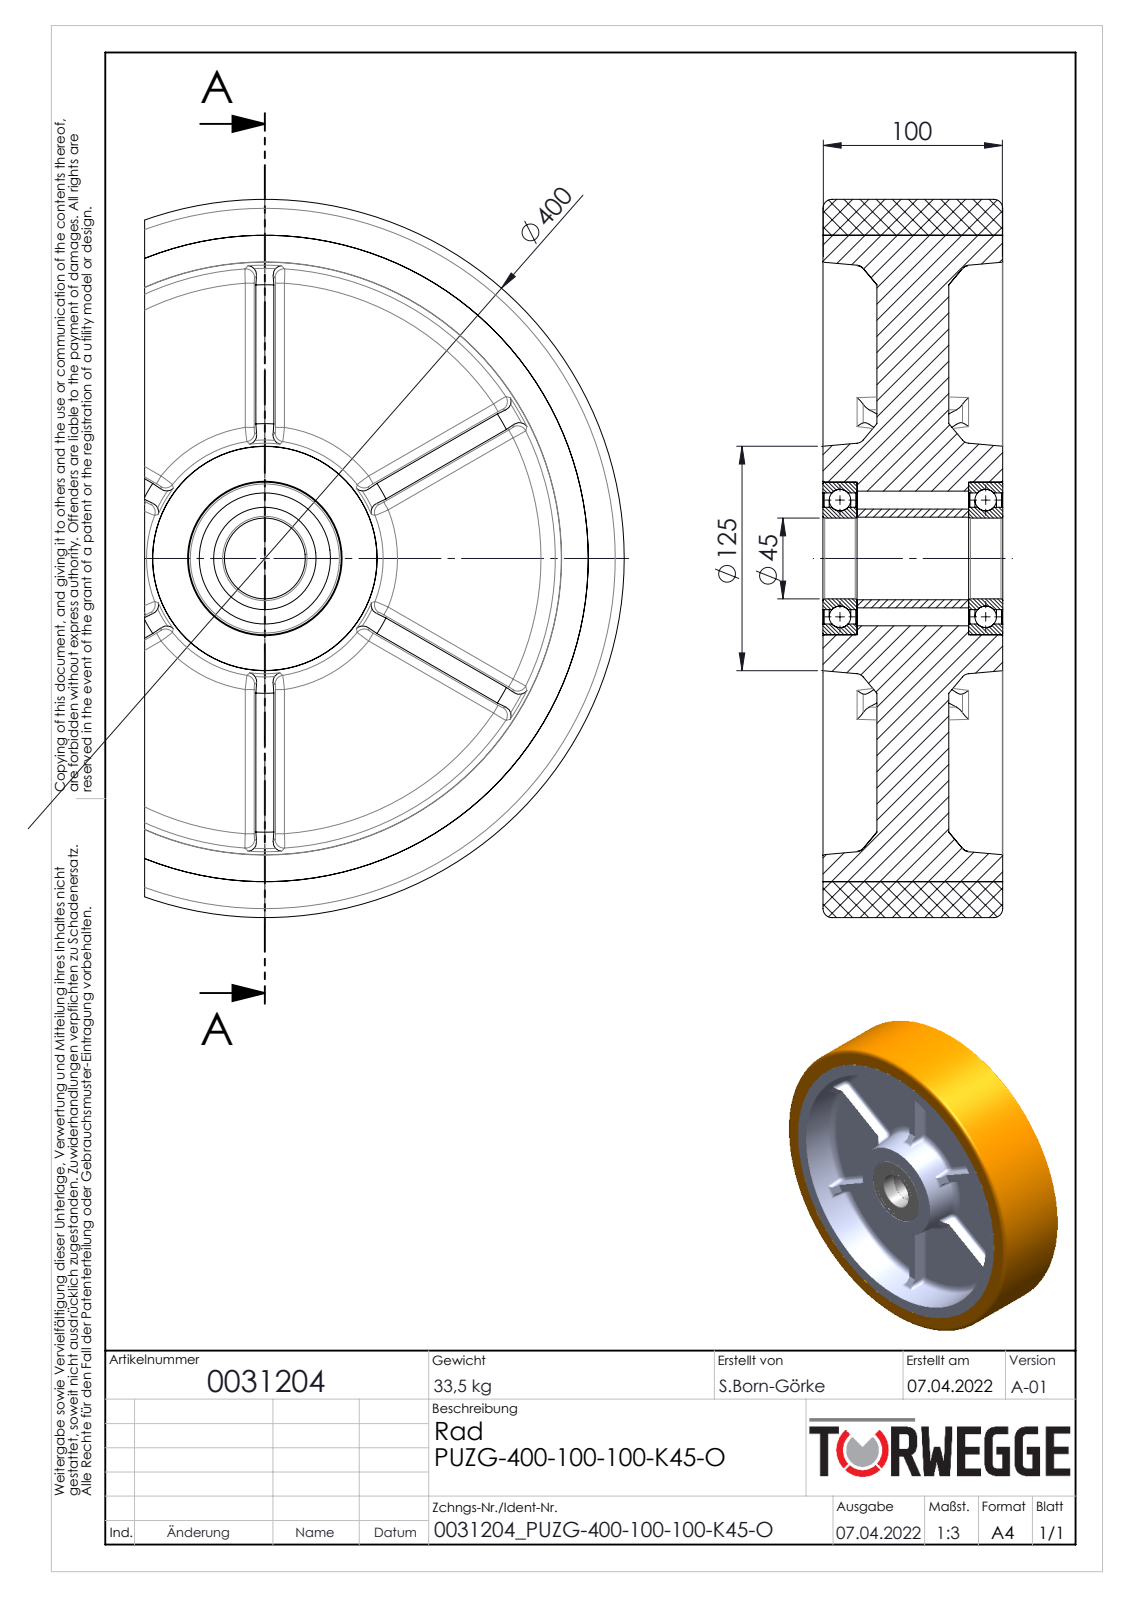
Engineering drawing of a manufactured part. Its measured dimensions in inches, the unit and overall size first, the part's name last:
Units: inches
Overall size (bounding box): 15.748 × 15.748 × 3.941
Round holes (diameter × count): ⌀1.772 ×1, ⌀1.811 ×1, ⌀2.244 ×1, ⌀2.874 ×1, ⌀2.953 ×1, ⌀3.346 ×1, ⌀14.173 ×1
Round bosses / shafts (diameter × count): ⌀15.748 ×1, ⌀2.165 ×1
Partial cylindrical surfaces — rounded edges, fillets, slot ends (radius × count): R0.197 ×16
Main face-to-face distances: 1.772, 2.165, 0.394, 3.937, 0.529, 3.193, 1.181, 2.756, 0.591, 0.984
Volume: 375.4 in³ · Surface area: 1 299 in²
Bodies: 13 solids, 386 faces (74 planar, 80 cylindrical, 232 other)
Part name (STEP PRODUCT): 0031204
STEP written by: SolidWorks 2020 (AUTOMOTIVE_DESIGN)
